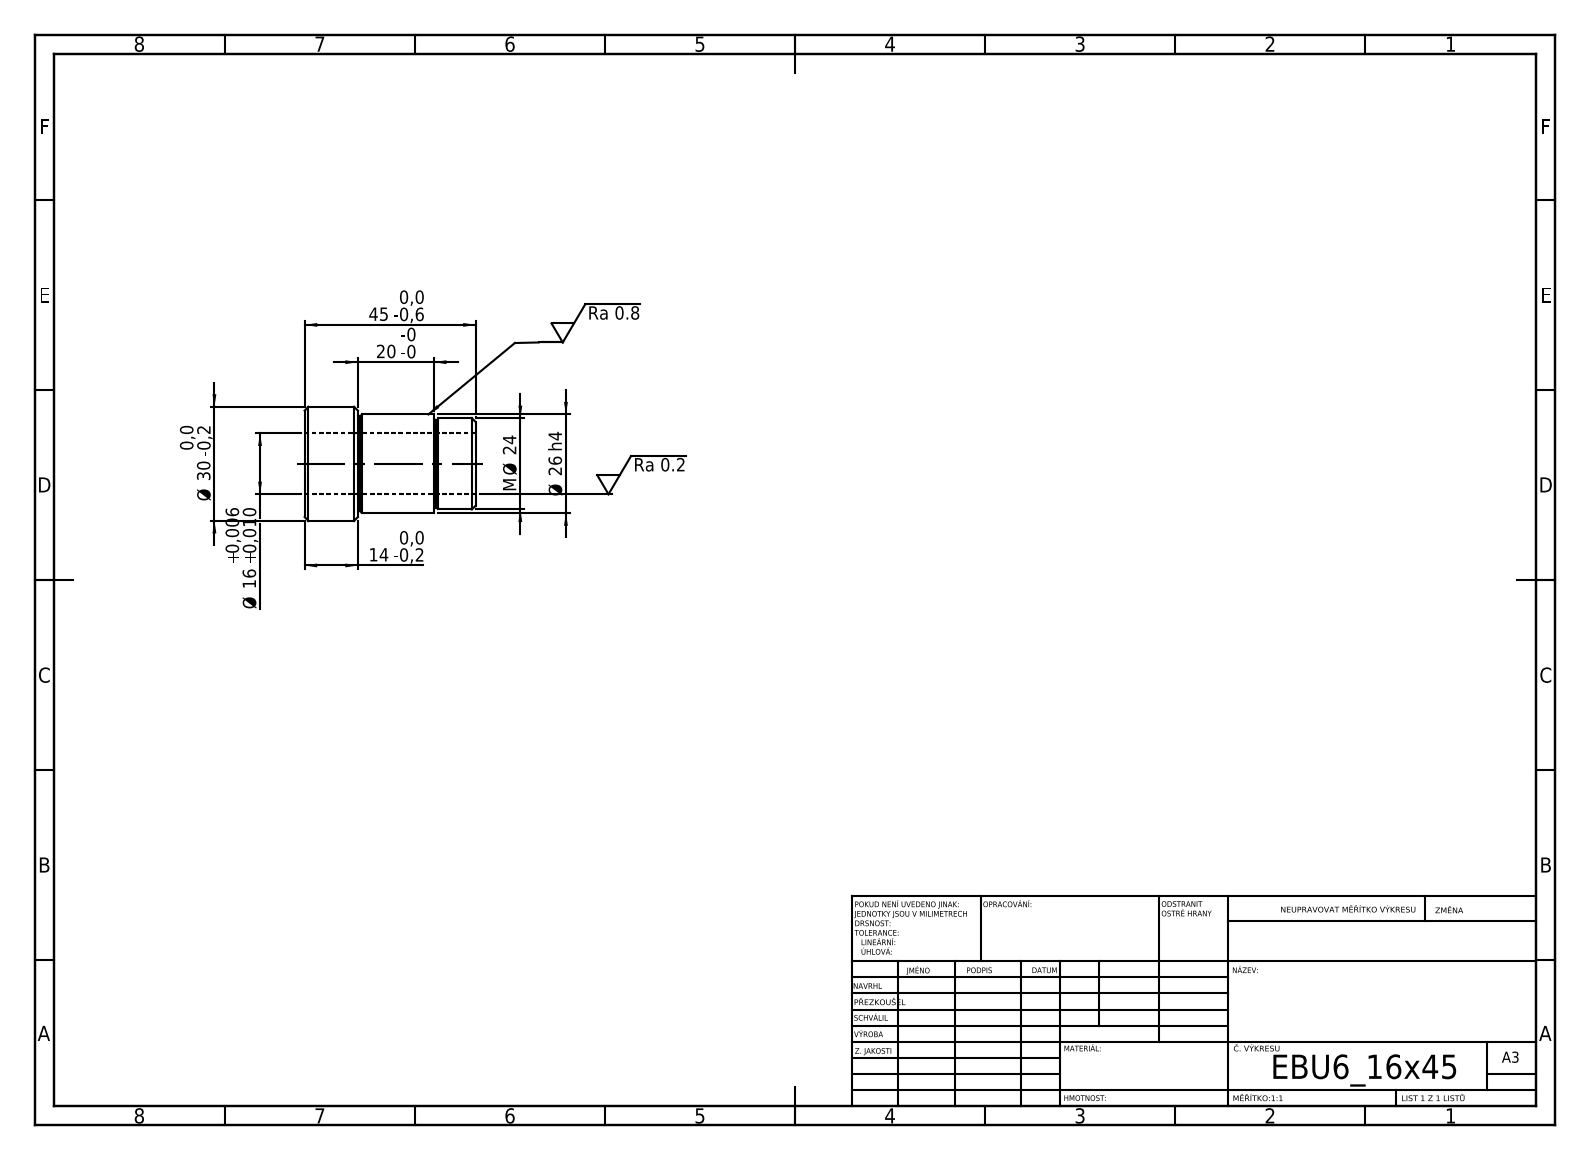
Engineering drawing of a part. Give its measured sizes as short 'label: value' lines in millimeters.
written by: SolidWorks 2019 (CONFIG_CONTROL_DESIGN)
unit: mm
bodies: 1 solid, 27 faces (5 planar, 12 cylindrical, 10 other)
size: 45 × 30 × 30
volume: 16 245 mm³; area: 7 013 mm²
holes: 1× ⌀16
bosses: 1× ⌀30, 1× ⌀26, 1× ⌀25, 1× ⌀24, 1× ⌀23
face distances: 45, 31, 14, 11, 20, 34, 10, 1, 21, 35
